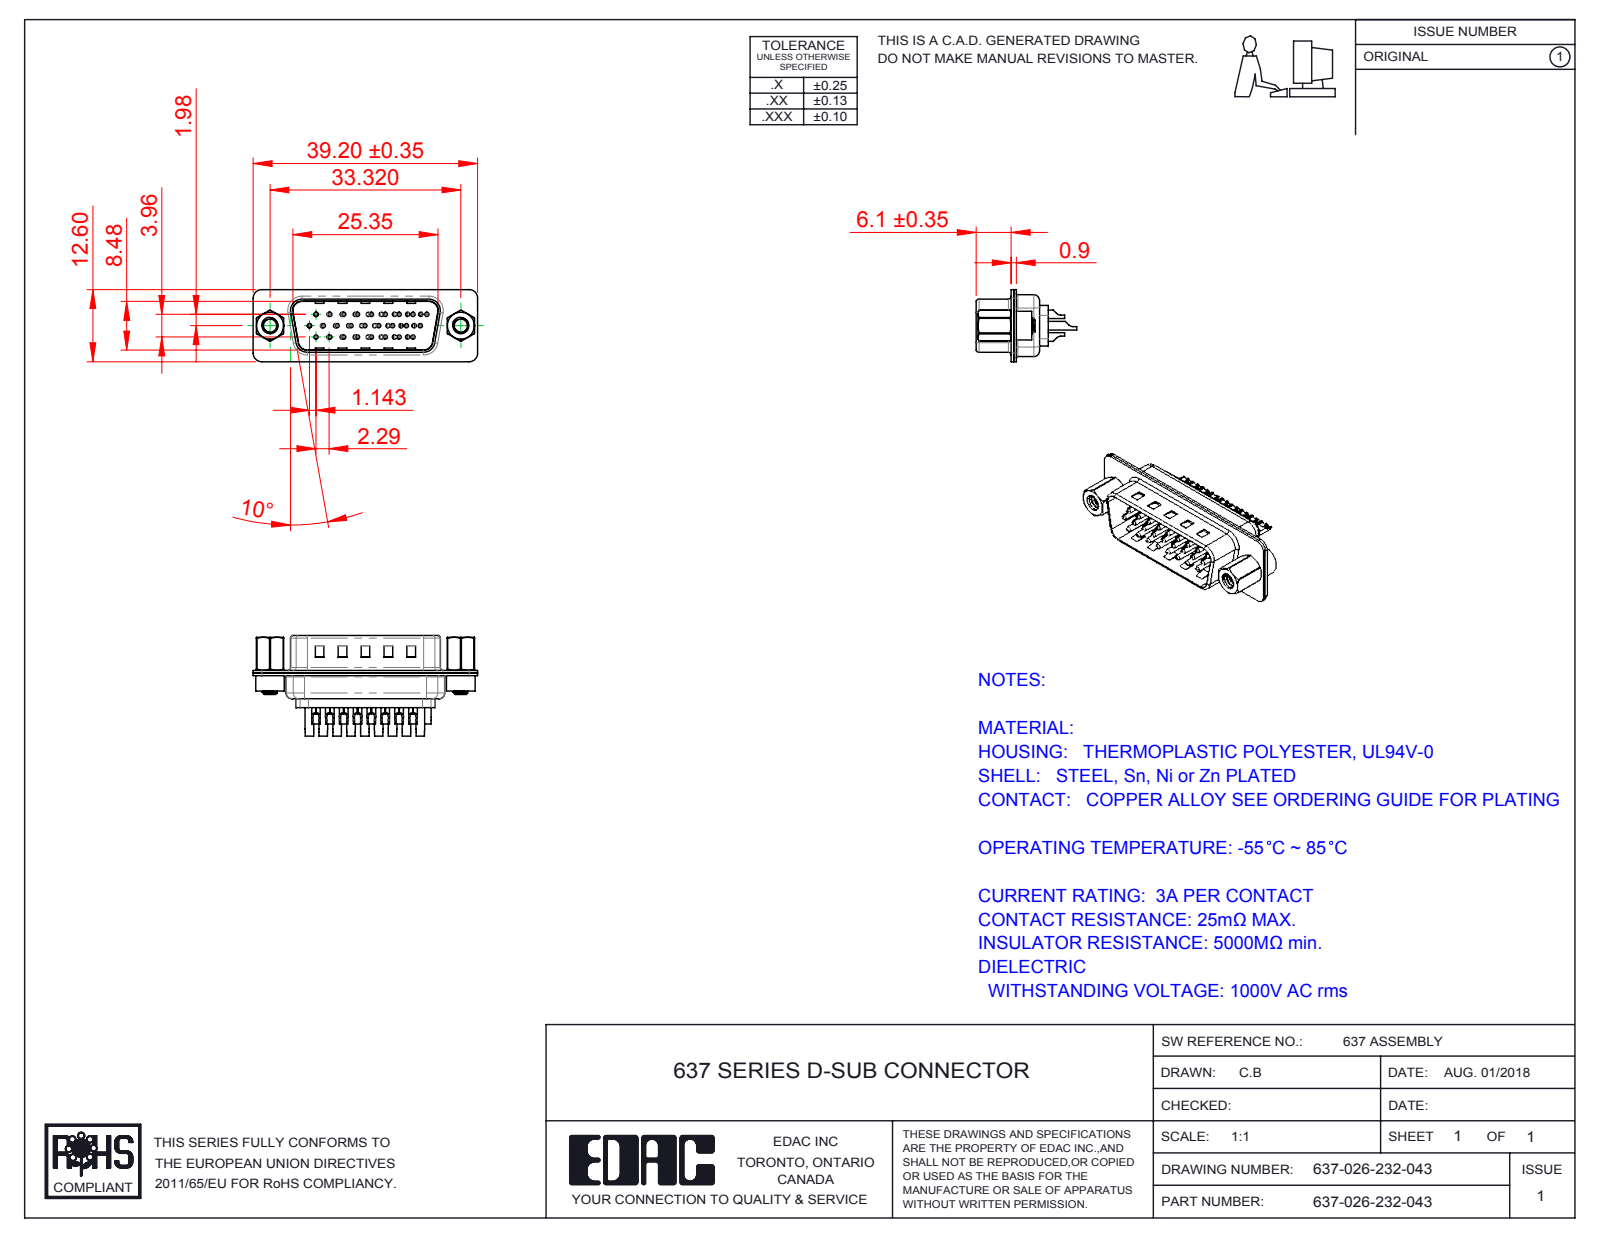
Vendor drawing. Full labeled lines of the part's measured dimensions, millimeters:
Part name (STEP PRODUCT): 637 Shell Rear_26 Contacts; 637 Housing_26 Contacts; 637 4-40 Threaded Rivet; 637 4-40 Hex Standoff (+5 more)
STEP written by: SolidWorks 2016 (CONFIG_CONTROL_DESIGN)
Units: millimetres
Bodies: 33 solids, 2130 faces (525 planar, 959 cylindrical, 646 other)
Overall size (bounding box): 39.2 × 17.55 × 12.6
Volume: 2 068 mm³ · Surface area: 7 410 mm²
Round holes (diameter × count): ⌀1.6 ×49, ⌀0.35 ×26, ⌀1.1 ×26, ⌀0.75 ×23, ⌀2 ×23, ⌀2.26 ×2, ⌀2.29 ×2, ⌀4 ×2, ⌀4.8 ×2
Round bosses / shafts (diameter × count): ⌀2 ×26, ⌀1.5 ×26, ⌀0.75 ×26, ⌀5 ×2, ⌀4.9 ×2, ⌀2.79 ×2
Partial cylindrical surfaces — rounded edges, fillets, slot ends (radius × count): R1.5 ×16, R2 ×12, R0.5 ×8, R1 ×7, R0.25 ×4, R0.55 ×4, R0.7 ×4, R0.95 ×4
Main face-to-face distances: 0.45, 0.4, 0.9, 8.48, 0.7, 8.88, 0.31, 4.55, 1.05, 1.16
Hole centre spacings: 3.96, 2.28, 4.57, 6.05, 2.29, 8.24, 6.86, 10.48
